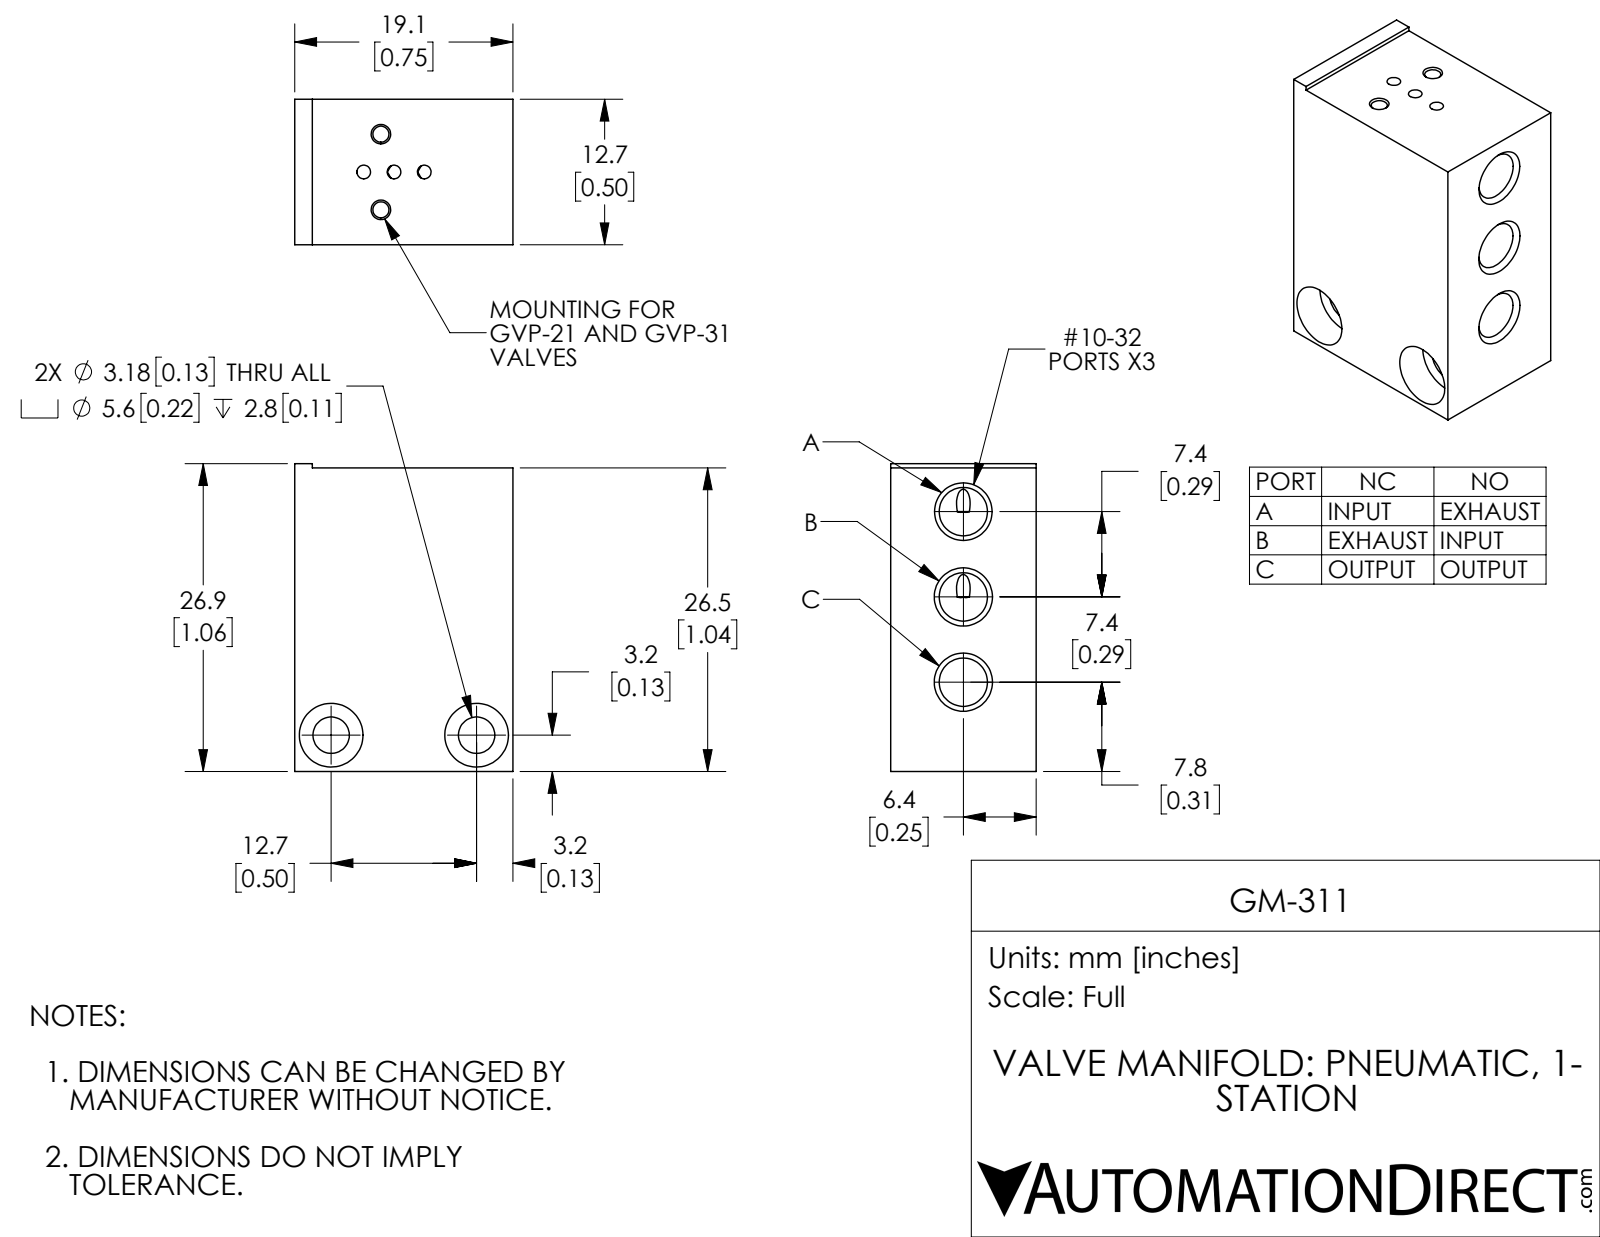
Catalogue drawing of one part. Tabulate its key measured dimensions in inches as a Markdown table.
| quantity | value |
| --- | --- |
| part name | GM-311 |
| STEP written by | SolidWorks 2018 (AUTOMOTIVE_DESIGN) |
| units | inches |
| bodies | 1 solid, 56 faces (10 planar, 24 cylindrical, 22 other) |
| overall size | 1.058 × 0.75 × 0.5 |
| volume | 0.343 in³ |
| surface area | 4.651 in² |
| round holes (diameter × count) | 0.047 × 3, 0.166 × 3, 0.055 × 2, 0.125 × 2, 0.219 × 2 |
| main face-to-face distances | 0.5, 0.75, 1.043, 0.388, 0.112, 1.058, 0.015, 0.06, 0.69 |
| hole center spacings | 0.104, 0.137, 0.143, 0.198, 0.293, 0.208, 0.26, 0.5 |
